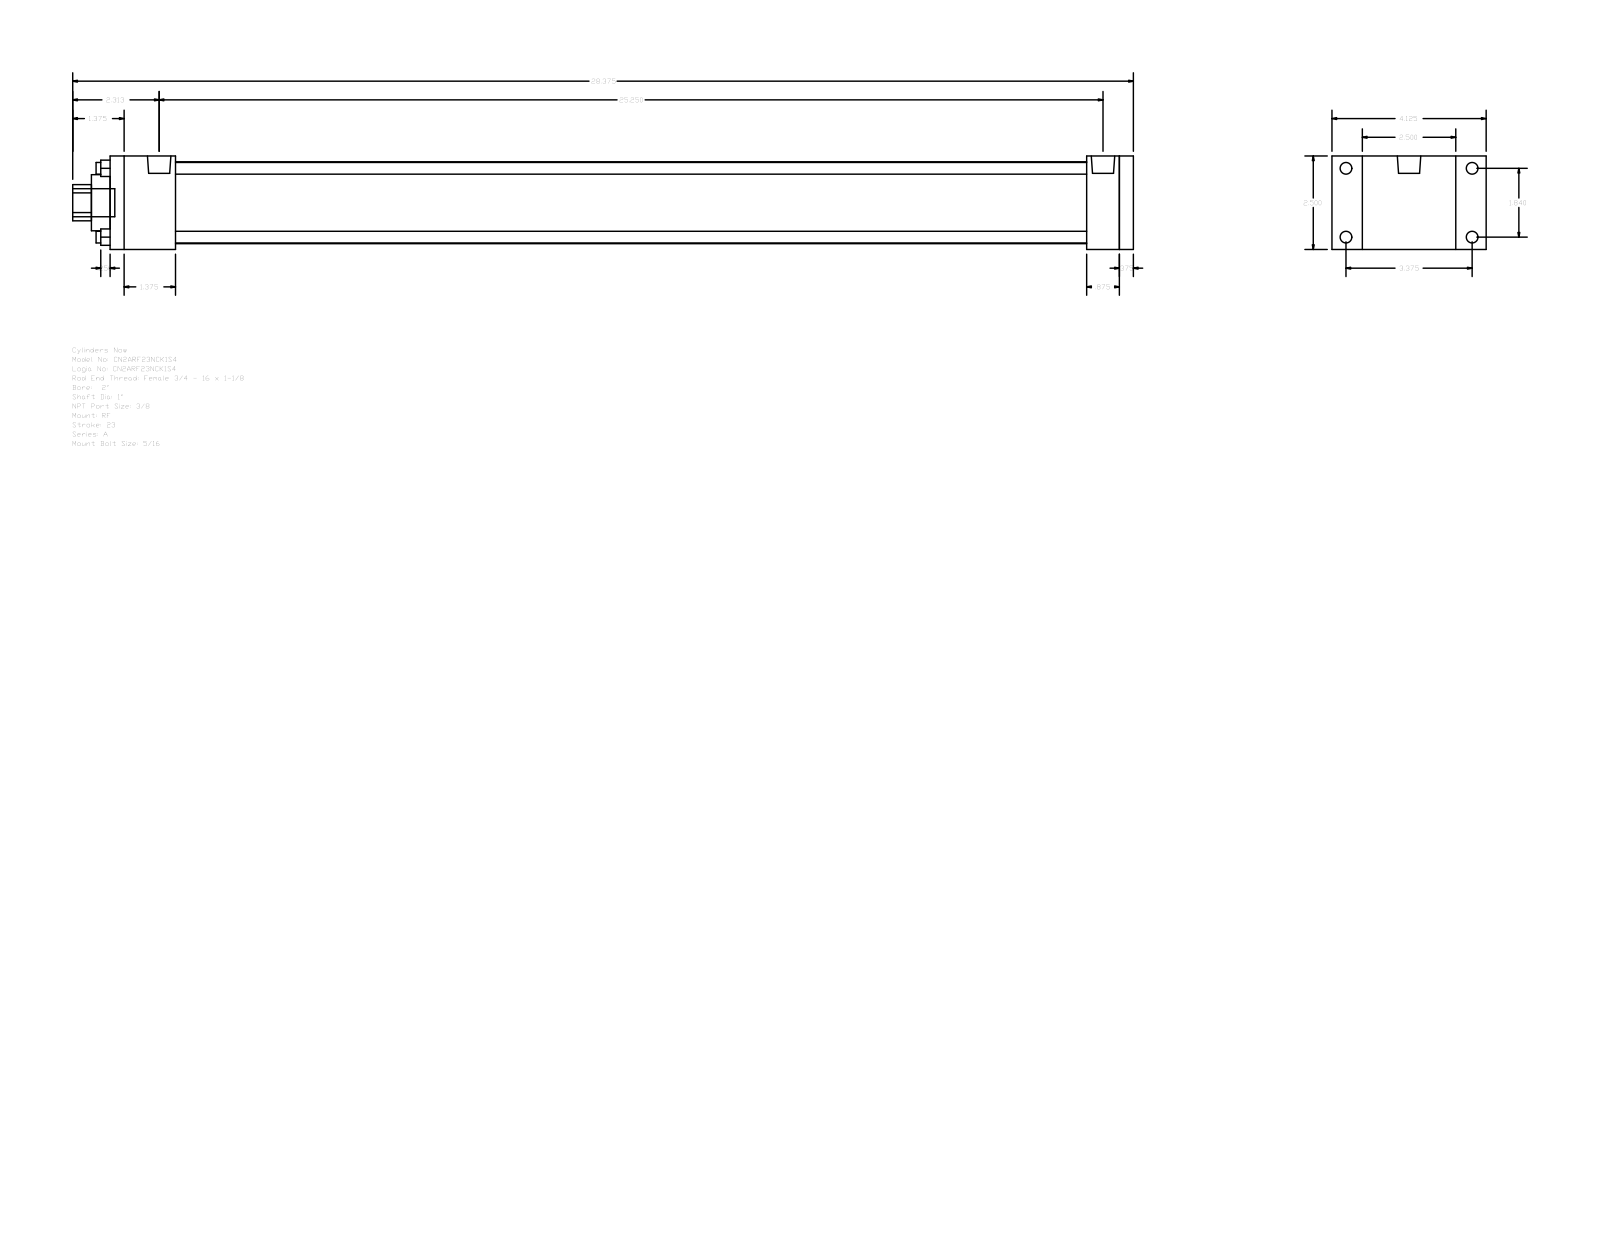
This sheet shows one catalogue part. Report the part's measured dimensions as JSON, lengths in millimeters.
{"part_name": "A_RF__0200_1", "step_written_by": "GSSL Pune (CONFIG_CONTROL_DESIGN)", "units": "millimeters", "bodies": {"solids": 0, "faces": 92, "planar": 64, "cylindrical": 28, "other": 0}, "overall_size": [720.73, 104.78, 63.5], "round_holes": [[7.94, 4], [25.4, 1], [38.1, 1], [55.63, 1]], "round_bosses_or_shafts": [[7.94, 4], [5.56, 4], [15.93, 2], [19.05, 1]], "partial_cylinders_radius": [[12.29, 1]], "face_to_face_distances": [63.5, 9.53, 695.33, 685.8, 20.64, 44.45, 641.35, 650.88, 663.58, 619.13], "hole_center_spacings": [33.05, 46.74, 66.1]}
